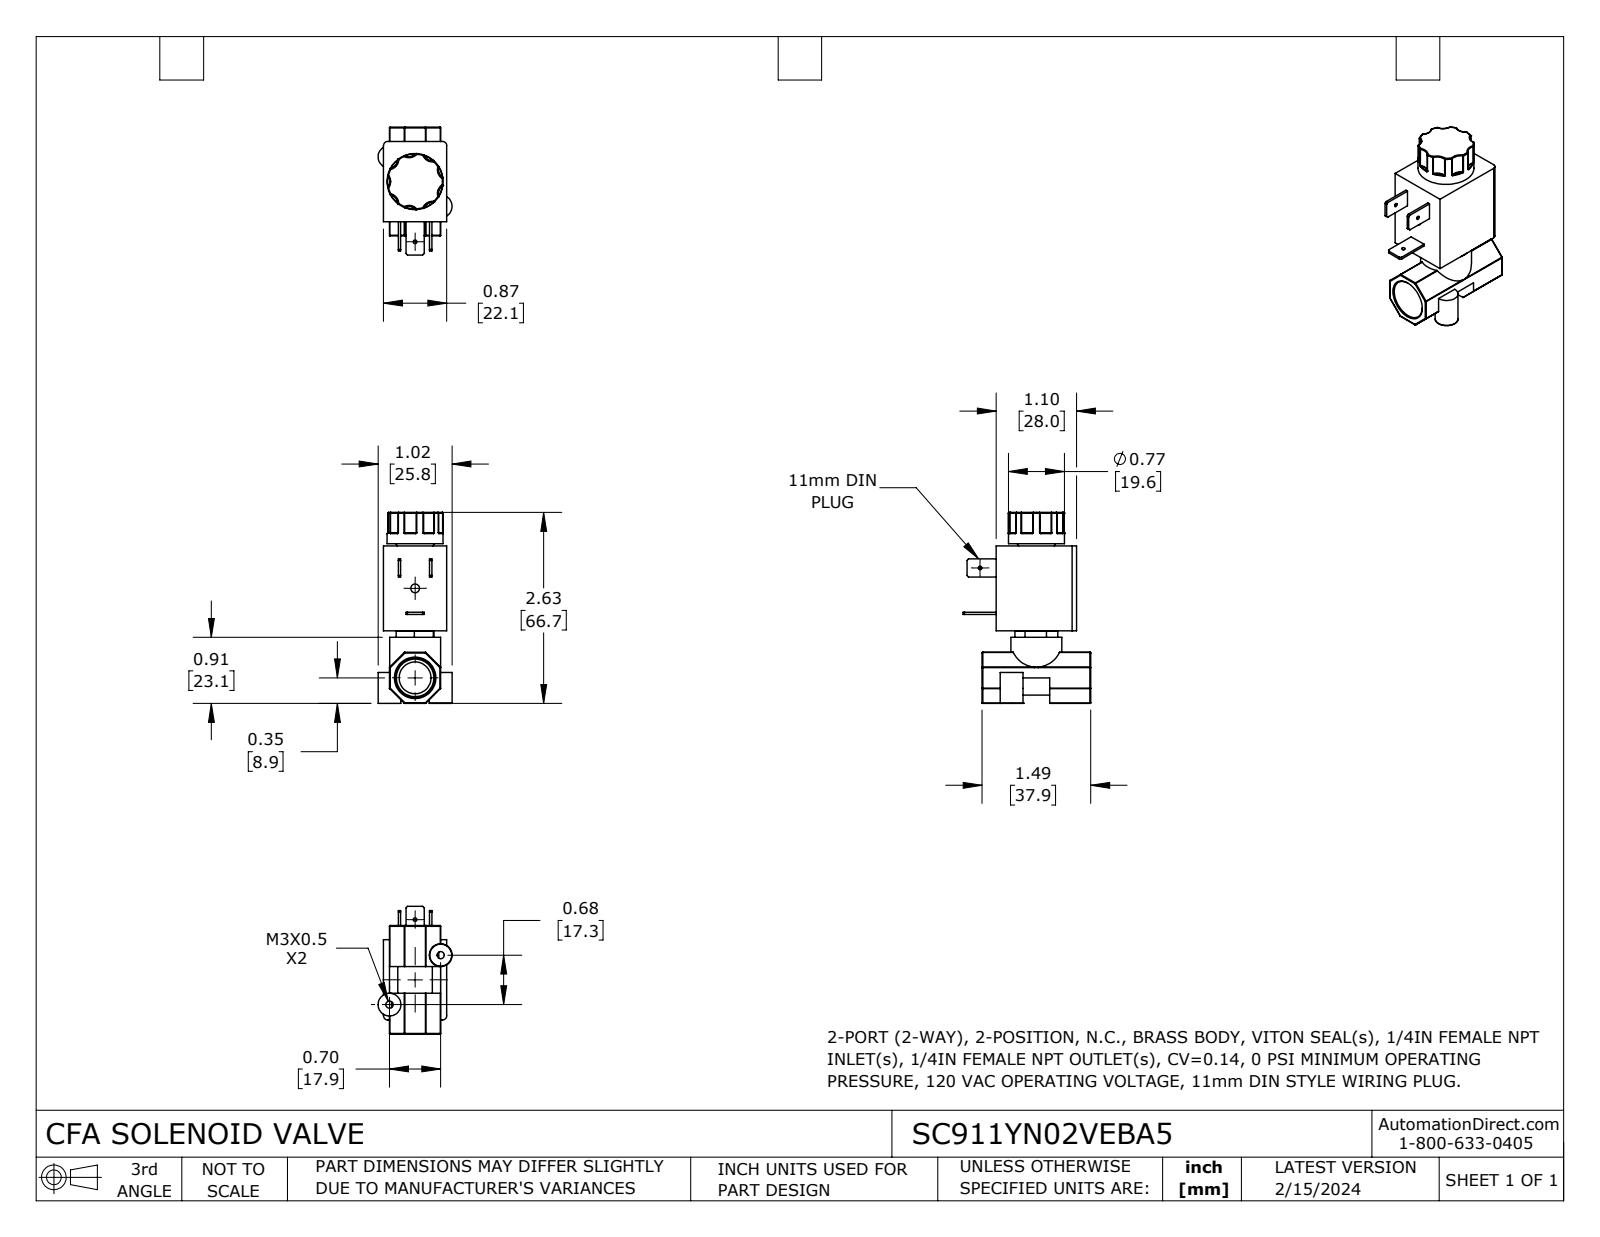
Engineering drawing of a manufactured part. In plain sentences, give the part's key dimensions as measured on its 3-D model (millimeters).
The part is named "SC911YN02VEBA5". Its 3-D file was written by "SolidWorks 2023 (CONFIG_CONTROL_DESIGN)". It is 1 solid with 314 faces: 74 planar, 91 cylindrical and 149 other. Overall it measures 66.7 by 44.6 by 25.8 millimeters. Its volume is 29 460 cubic millimeters and its surface area 10 410 square millimeters. Round holes: 2 of diameter 1.3, 2 of diameter 2.5, 1 of diameter 3, 1 of diameter 11.1. Round bosses or shafts: 2 of diameter 8, 1 of diameter 19.6, 1 of diameter 17.8. Partial cylindrical surfaces (rounded edges, fillets, slot ends): 42 of radius 0.3, 7 of radius 3.4, 2 of radius 1.5, 2 of radius 3.4, 1 of radius 6, 1 of radius 8.3. The main face-to-face distances are 22.1, 17.9, 28, 29.6, 2.1, 20, 11.7, 25.3, 55, 66.7. The hole center spacings are 15.3, 24.9, 31, 31.2.
